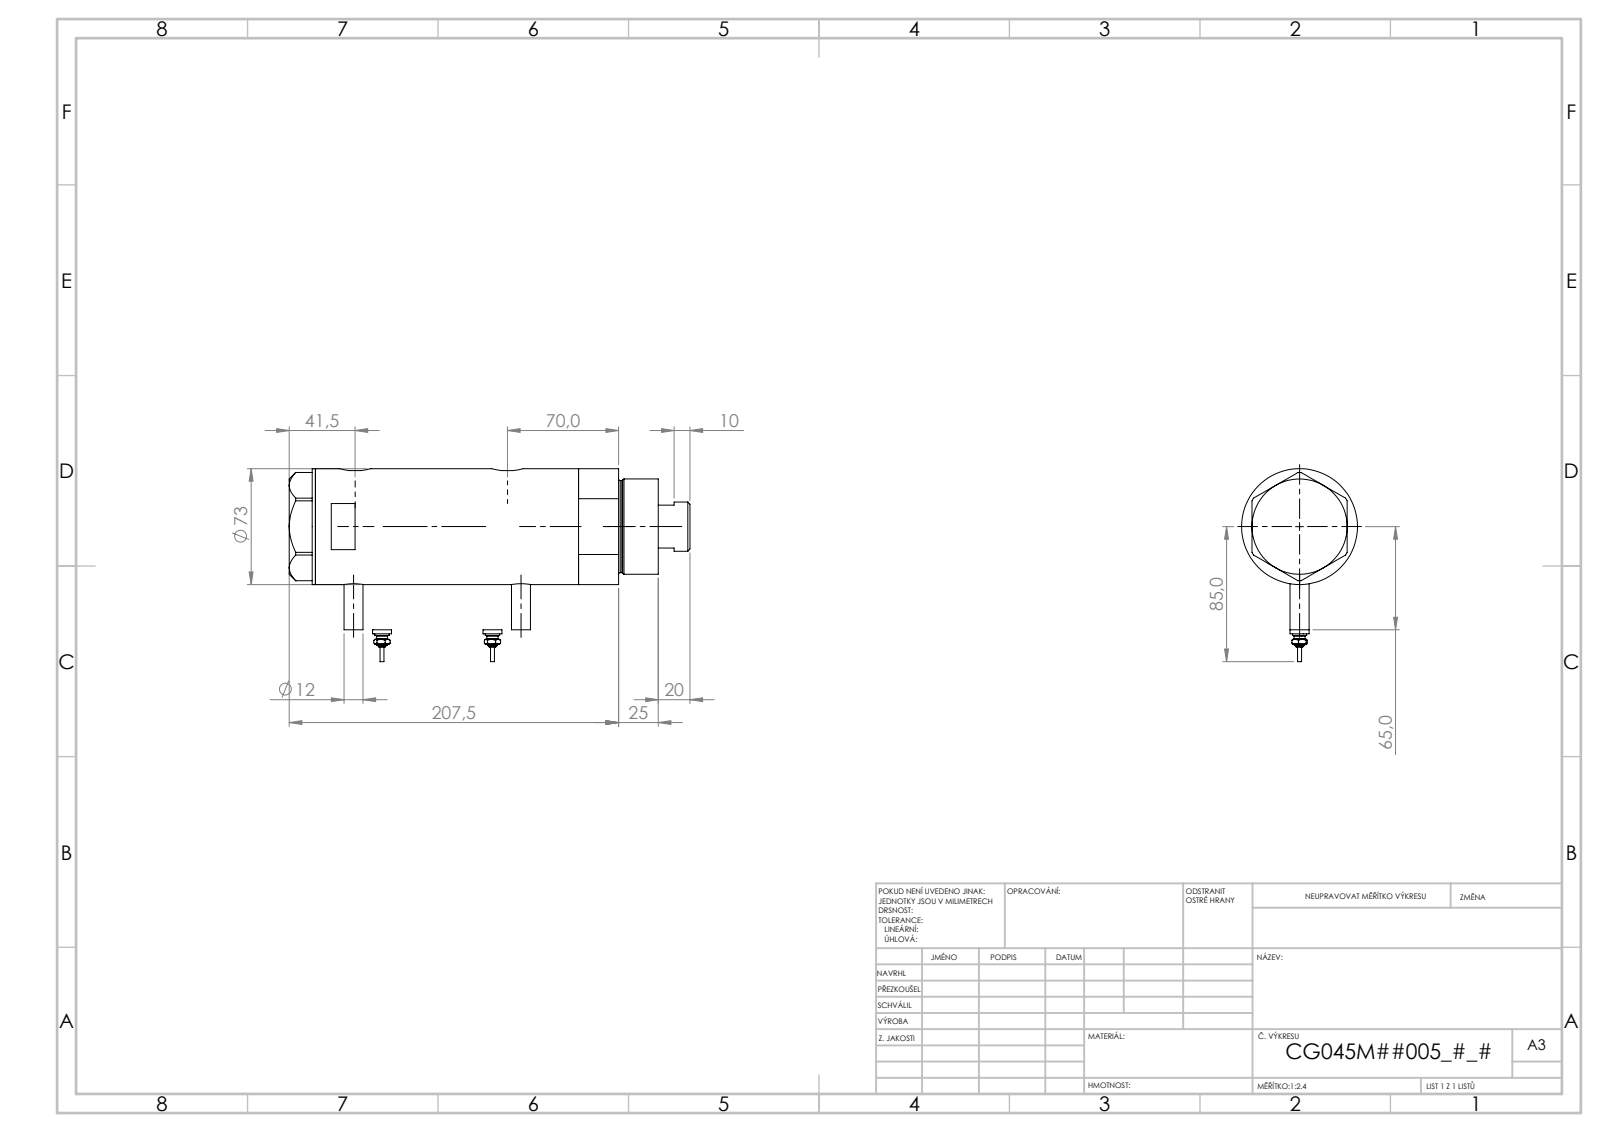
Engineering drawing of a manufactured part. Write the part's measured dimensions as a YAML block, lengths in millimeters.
part_name: "V270CG_VC; V270CG_BACK; V270CG_FRONT; Switch (+1 more)"
step_written_by: "SolidWorks 2019 (CONFIG_CONTROL_DESIGN)"
units: millimeters
bodies: {solids: 6, faces: 212, planar: 77, cylindrical: 71, other: 64}
overall_size: [252.5, 121.5, 73]
volume: 927537
surface_area: 153567
round_holes:
  - {diameter: 12.5, count: 2}
  - {diameter: 13.16, count: 2}
  - {diameter: 10.5, count: 1}
  - {diameter: 32, count: 1}
  - {diameter: 33.5, count: 1}
  - {diameter: 45, count: 1}
  - {diameter: 48, count: 1}
  - {diameter: 64, count: 1}
round_bosses_or_shafts:
  - {diameter: 12, count: 4}
  - {diameter: 9, count: 2}
  - {diameter: 7, count: 2}
  - {diameter: 4.5, count: 2}
  - {diameter: 2.5, count: 2}
  - {diameter: 73, count: 1}
  - {diameter: 60, count: 1}
  - {diameter: 58, count: 1}
partial_cylinders:
  - {radius: 10, count: 2}
face_to_face_distances: [95, 121, 26, 16.5, 42.5, 137.5, 2, 216, 232.5, 190]
hole_center_spacings: [1, 8.5, 96, 97, 104.5, 105.5]
